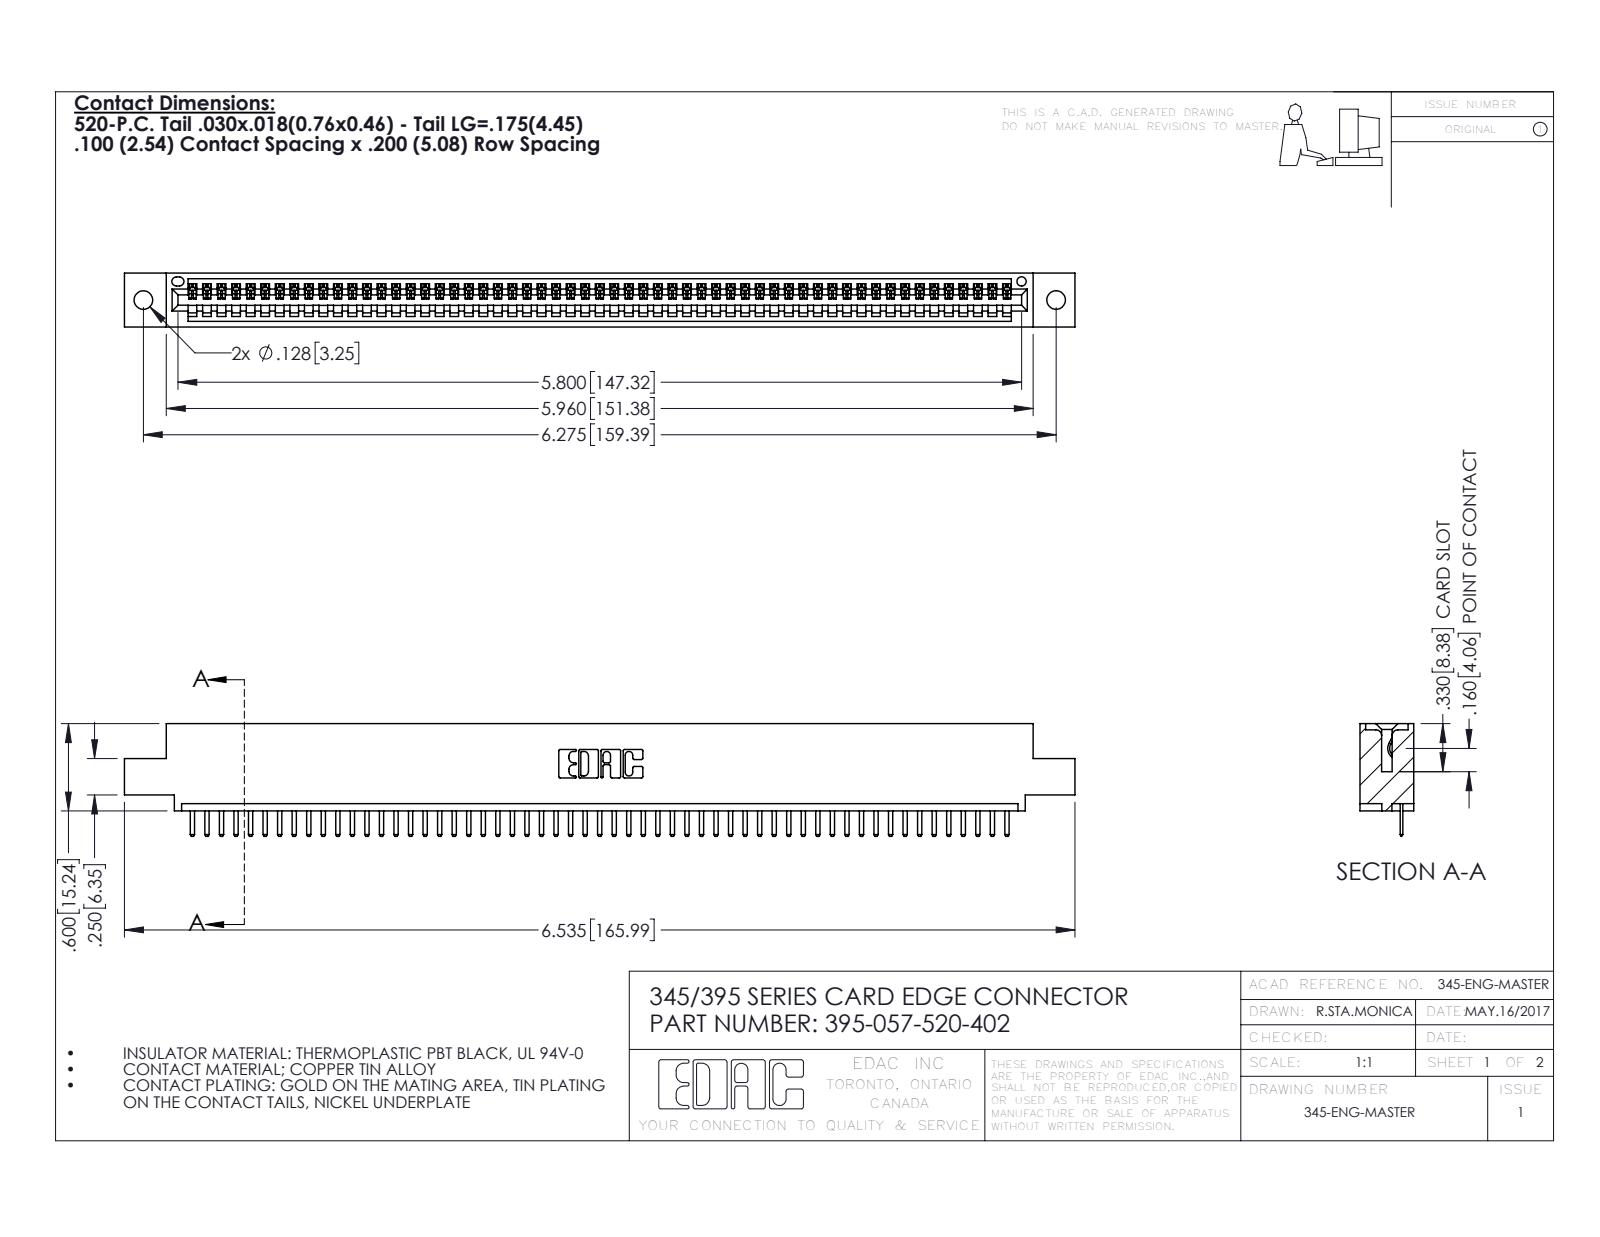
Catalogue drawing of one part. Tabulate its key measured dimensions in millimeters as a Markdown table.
| quantity | value |
| --- | --- |
| part name | 345-292-001_345-293-120; 345 Part_0.110 Offset - 0.128 Dia; 395-057-520-402 |
| STEP written by | SolidWorks 2016 (CONFIG_CONTROL_DESIGN) |
| units | millimeters |
| bodies | 58 solids, 3664 faces (2478 planar, 1186 cylindrical, 0 other) |
| overall size | 166 × 19.7 × 9.4 |
| volume | 15 600 mm³ |
| surface area | 20 230 mm² |
| round holes (diameter × count) | 3.3 × 2, 1.6 × 1 |
| partial cylindrical surfaces (radius × count) | 0.3 × 116, 0.2 × 114, 0.3 × 22, 0.2 × 6, 0.8 × 6, 0.7 × 3, 0.8 × 2, 1 × 2 |
| main face-to-face distances | 7.6, 1.8, 9.4, 5.1, 2.5, 6.9, 0.6, 5.7, 1.8, 3.8 |
| hole center spacings | 6.9, 153.4, 159.4 |
